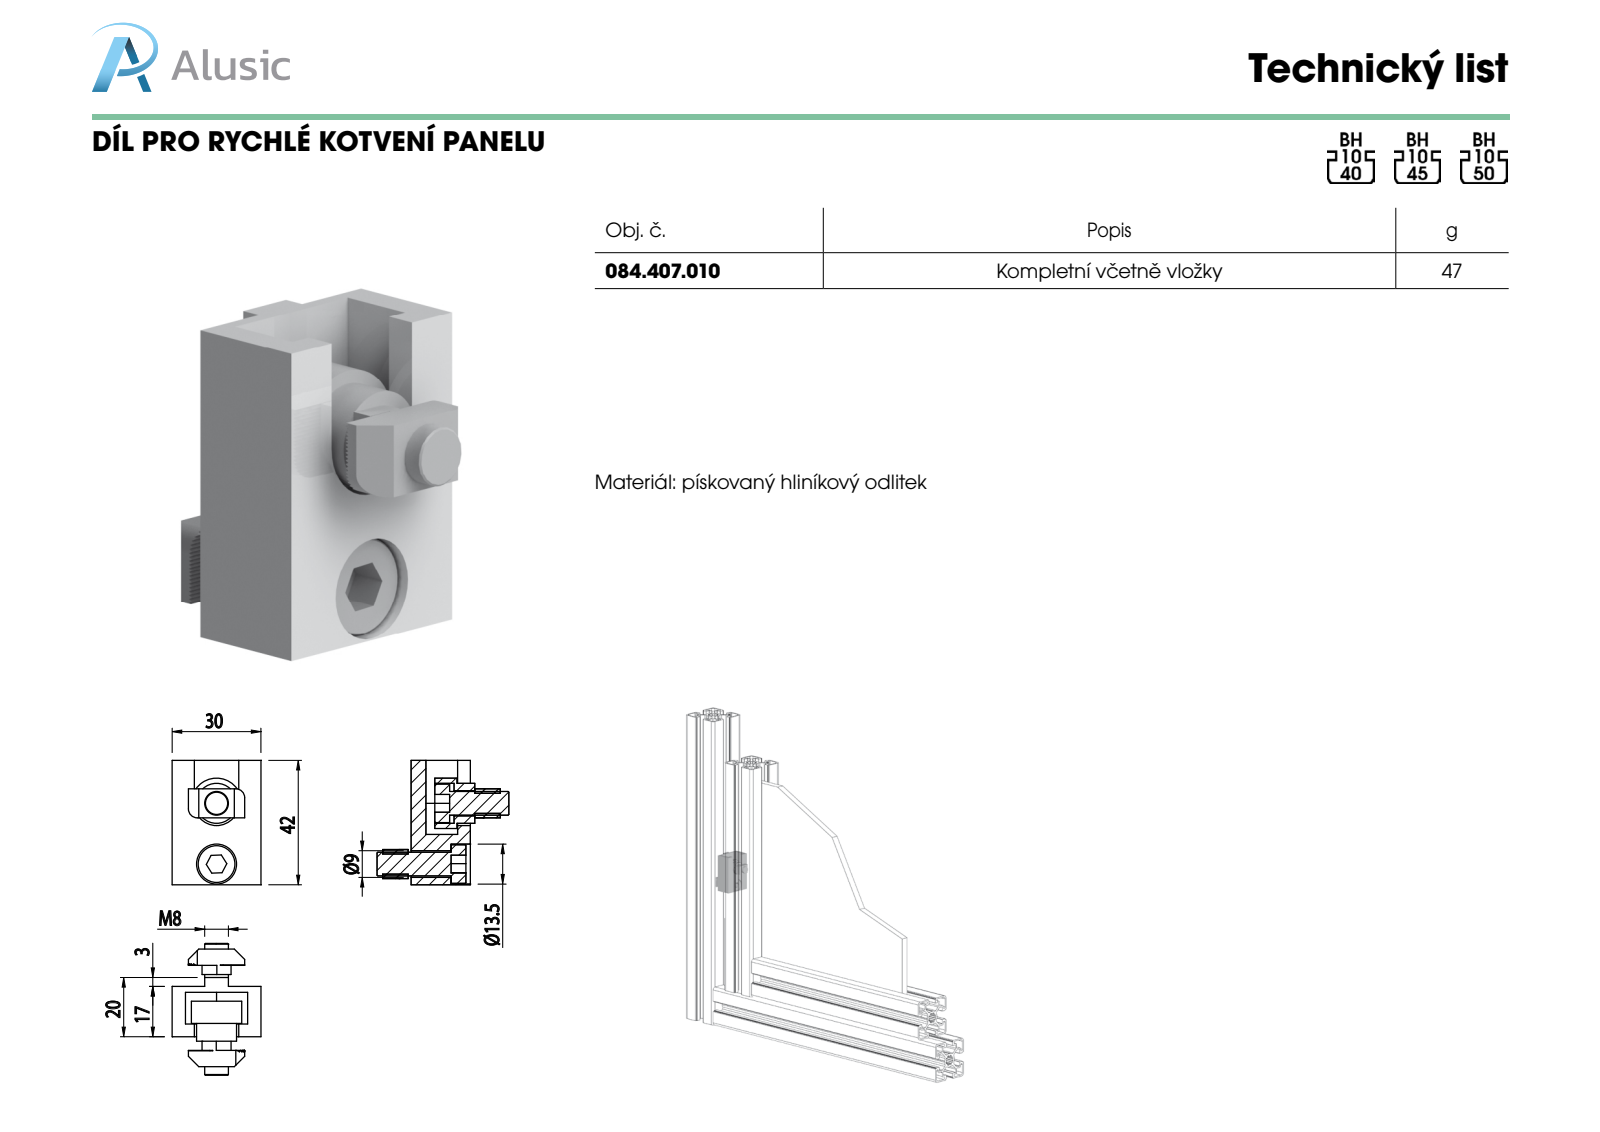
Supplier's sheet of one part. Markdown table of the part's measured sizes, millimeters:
| quantity | value |
| --- | --- |
| part name | 084.407.001b; 084.301.000 VITI ALUSIC_084.301.003; 084.407.010; 084.302.028 (+2 more) |
| STEP written by | SolidWorks 2016 (CONFIG_CONTROL_DESIGN) |
| units | millimeters |
| bodies | 6 solids, 408 faces (328 planar, 72 cylindrical, 8 other) |
| overall size | 44.5 × 42 × 30 |
| volume | 20 367 mm³ |
| surface area | 12 354 mm² |
| round holes (diameter × count) | 6.8 × 2, 13.5 × 2, 8.5 × 1, 9 × 1 |
| round bosses / shafts (diameter × count) | 13 × 2, 8 × 2, 17 × 1 |
| partial cylindrical surfaces (radius × count) | 3 × 4, 5 × 4, 7.5 × 1, 10.5 × 1 |
| main face-to-face distances | 17, 30, 3, 5, 2, 15, 8, 6.5, 13.5, 5.5 |
| hole center spacings | 20.5 |
